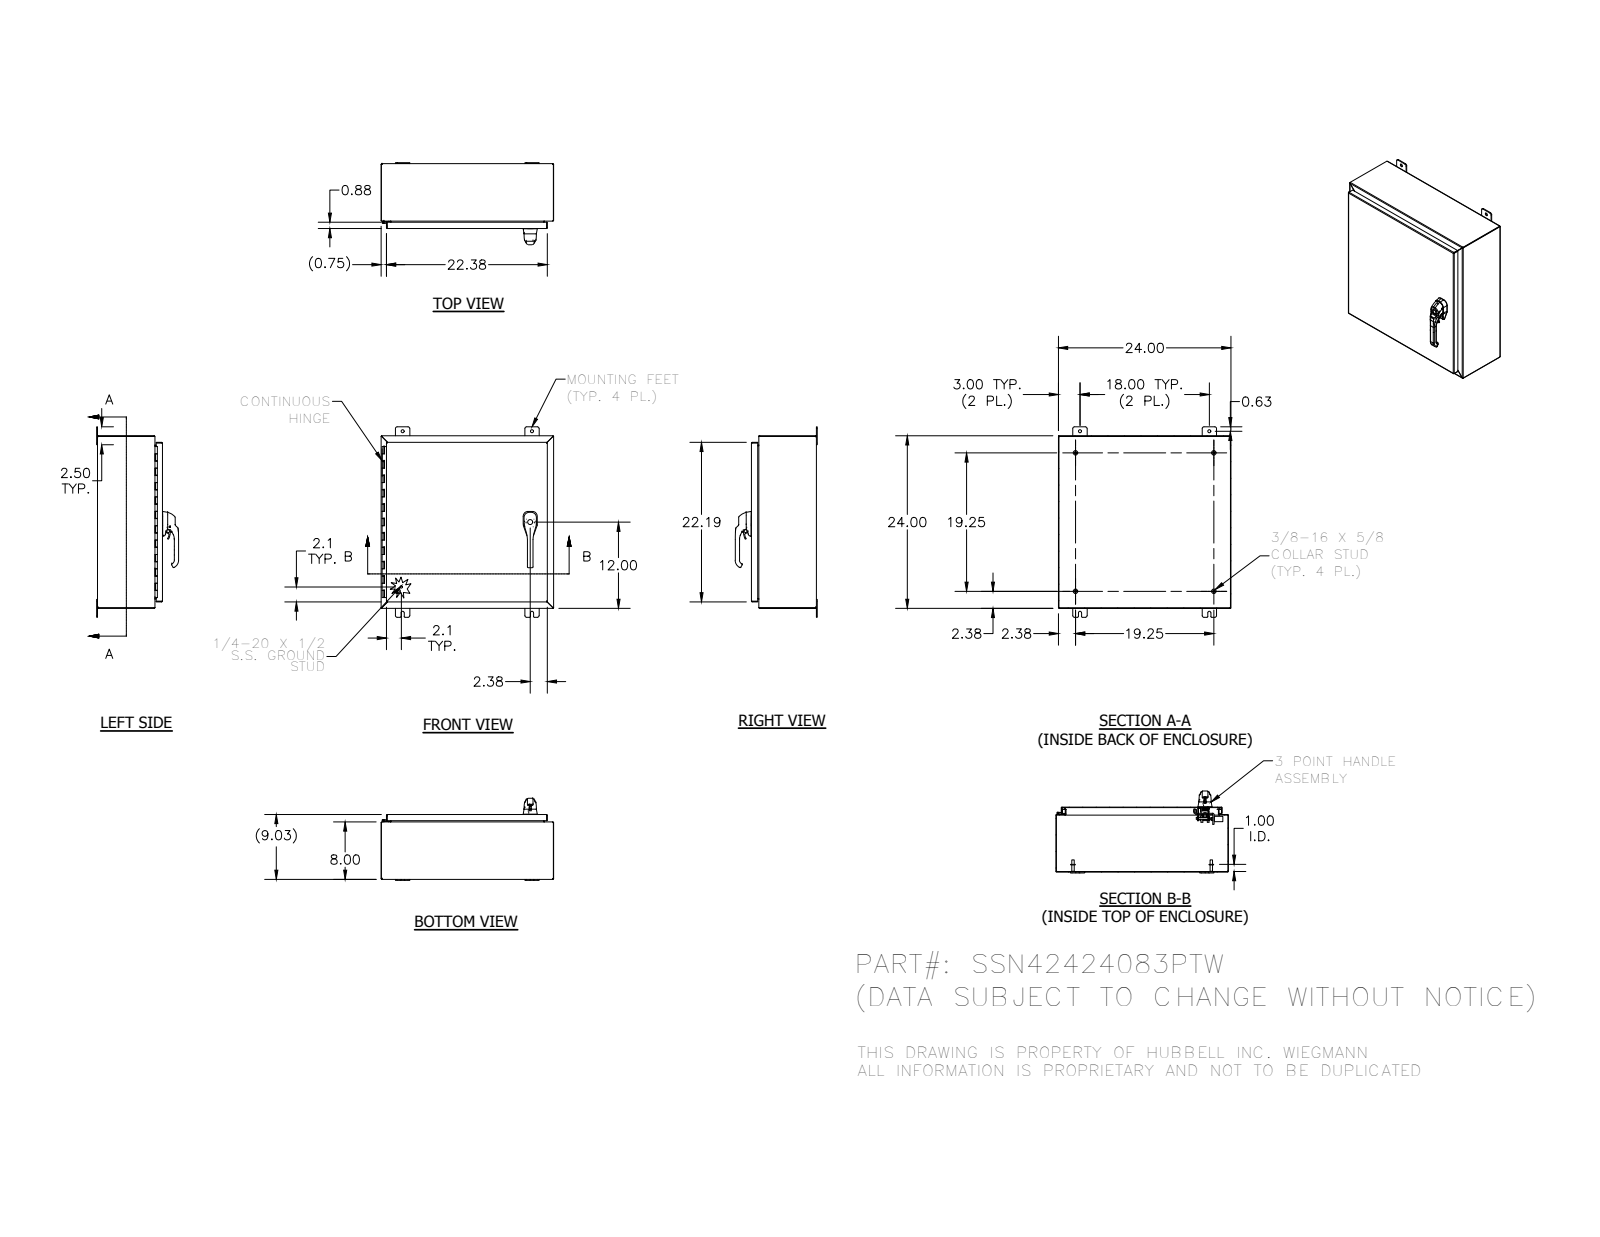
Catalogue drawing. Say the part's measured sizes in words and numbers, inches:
The part is named "LOCK-NUT_AF0; SSN42424083PTW; PLASTIC-ROLLER-CAM_AF1; SUPPORT-ROLL_AF0 (+8 more)". Its 3-D file was written by "SolidWorks 2014 (AUTOMOTIVE_DESIGN)". It is 56 solids with 3059 faces: 1014 planar, 1260 cylindrical and 785 other. Overall it measures 26.5 by 24 by 11.408 inches. Its volume is 184.2 cubic inches and its surface area 4 728 square inches. Round holes: 8 of diameter 0.262, 4 of diameter 0.187, 4 of diameter 0.438, 3 of diameter 0.213, 3 of diameter 0.281, 2 of diameter 0.241, 2 of diameter 0.25, 2 of diameter 0.252, 2 of diameter 0.315, 2 of diameter 0.4, 2 of diameter 0.402, 2 of diameter 0.413. Round bosses or shafts: 4 of diameter 0.625, 4 of diameter 0.33, 3 of diameter 0.236, 2 of diameter 1, 2 of diameter 0.563, 2 of diameter 0.533, 2 of diameter 0.531, 2 of diameter 0.5. Partial cylindrical surfaces (rounded edges, fillets, slot ends): 172 of radius 0.02, 113 of radius 0.012, 26 of radius 0.125, 24 of radius 0.031, 21 of radius 0.019, 20 of radius 0.105, 20 of radius 0.25, 16 of radius 0.025. The main face-to-face distances are 0.074, 8.959, 23.926, 8.885, 9.033, 23.852, 24, 7.926, 1.033, 8. The hole center spacings are 0.38, 0.492, 0.76, 0.886, 14.428, 0.234, 0.258, 0.38.
